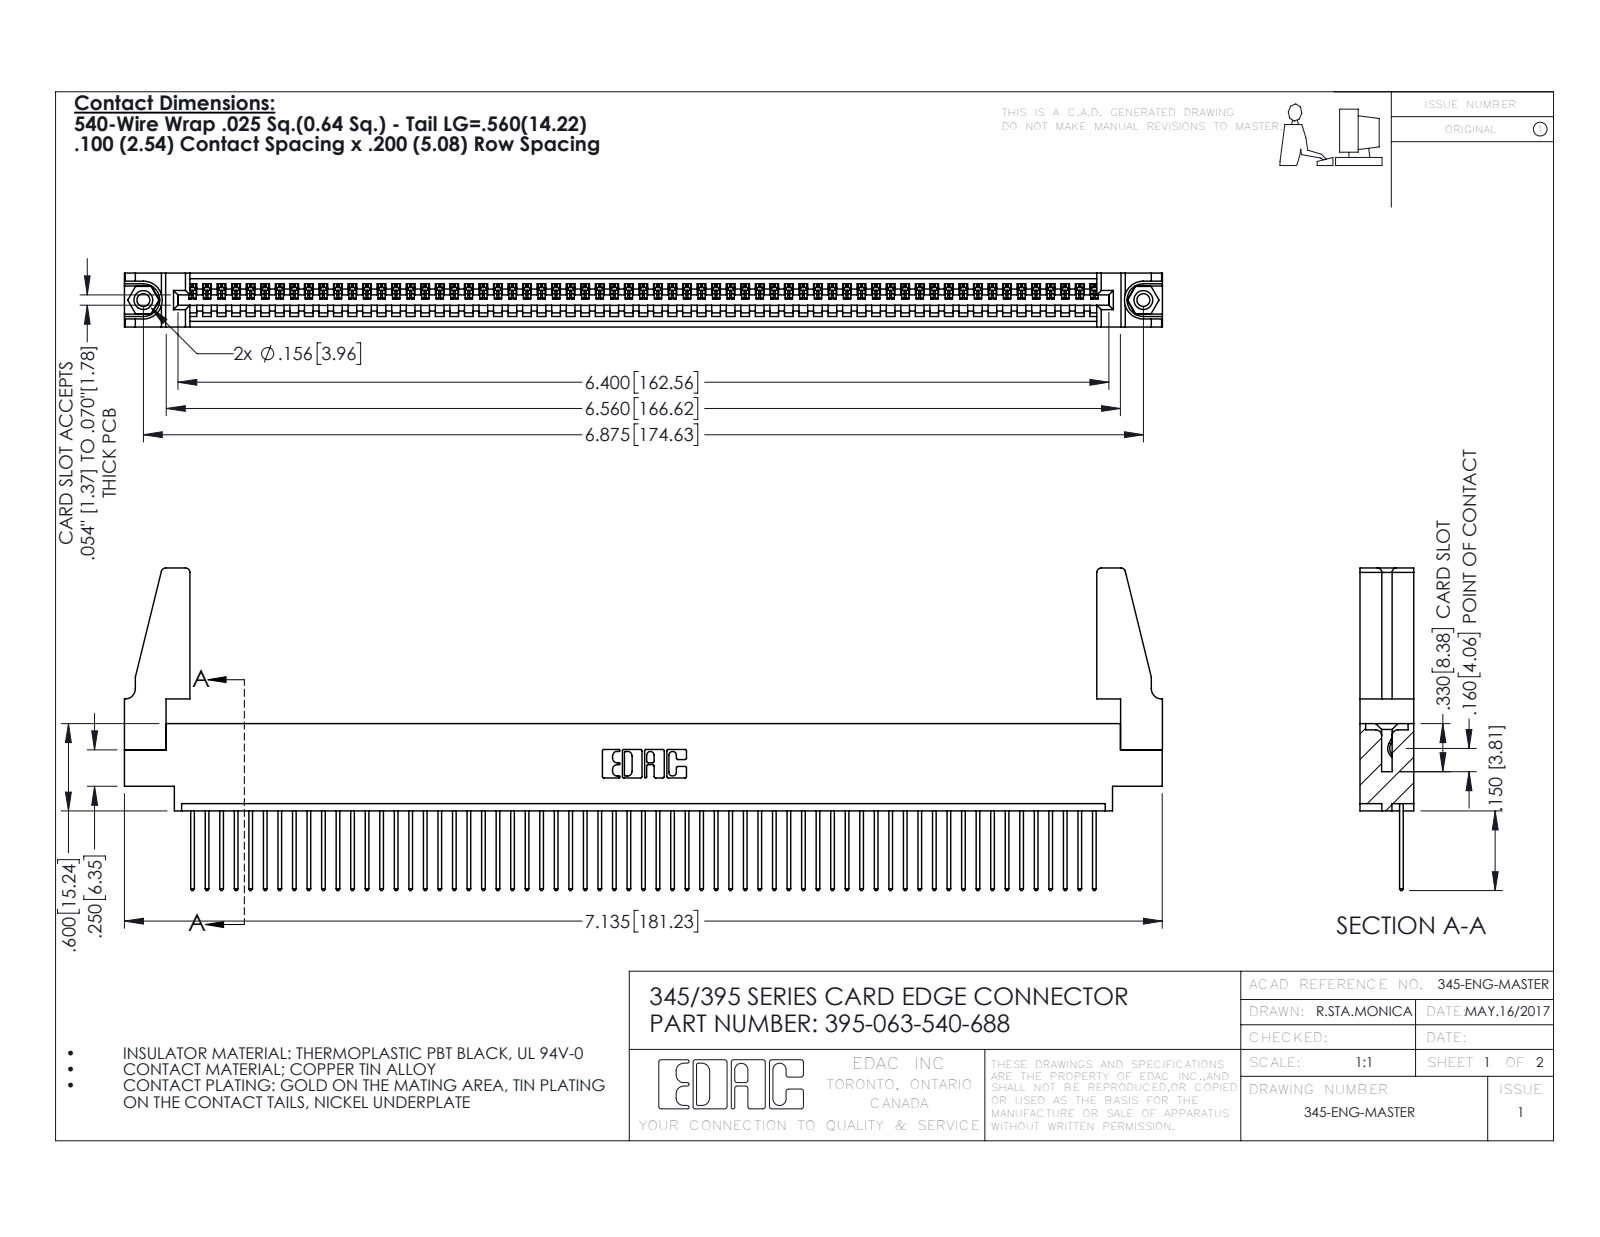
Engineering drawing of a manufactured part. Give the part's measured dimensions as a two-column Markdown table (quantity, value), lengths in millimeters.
| quantity | value |
| --- | --- |
| part name | 345-292-001_345-293-140; 345-250-001_345-250-001-102; 345-220-078_345-220-088; 395-063-540-688 (+1 more) |
| STEP written by | SolidWorks 2016 (CONFIG_CONTROL_DESIGN) |
| units | millimeters |
| bodies | 68 solids, 3908 faces (2676 planar, 1216 cylindrical, 16 other) |
| overall size | 181.3 × 56.3 × 9.4 |
| volume | 20 610 mm³ |
| surface area | 27 230 mm² |
| round holes (diameter × count) | 2.3 × 2, 3.2 × 2, 4 × 2, 1.6 × 1 |
| round bosses / shafts (diameter × count) | 3.9 × 2 |
| partial cylindrical surfaces (radius × count) | 0.2 × 126, 0.3 × 126, 0.3 × 22, 0.8 × 8, 0.2 × 6, 0.8 × 6, 0.7 × 3, 0.8 × 2 |
| main face-to-face distances | 1.8, 7.6, 9.4, 2.5, 6.9, 0.6, 5.1, 5.7, 4.4, 3.8 |
| hole center spacings | 6.9, 168.6, 174.6 |
